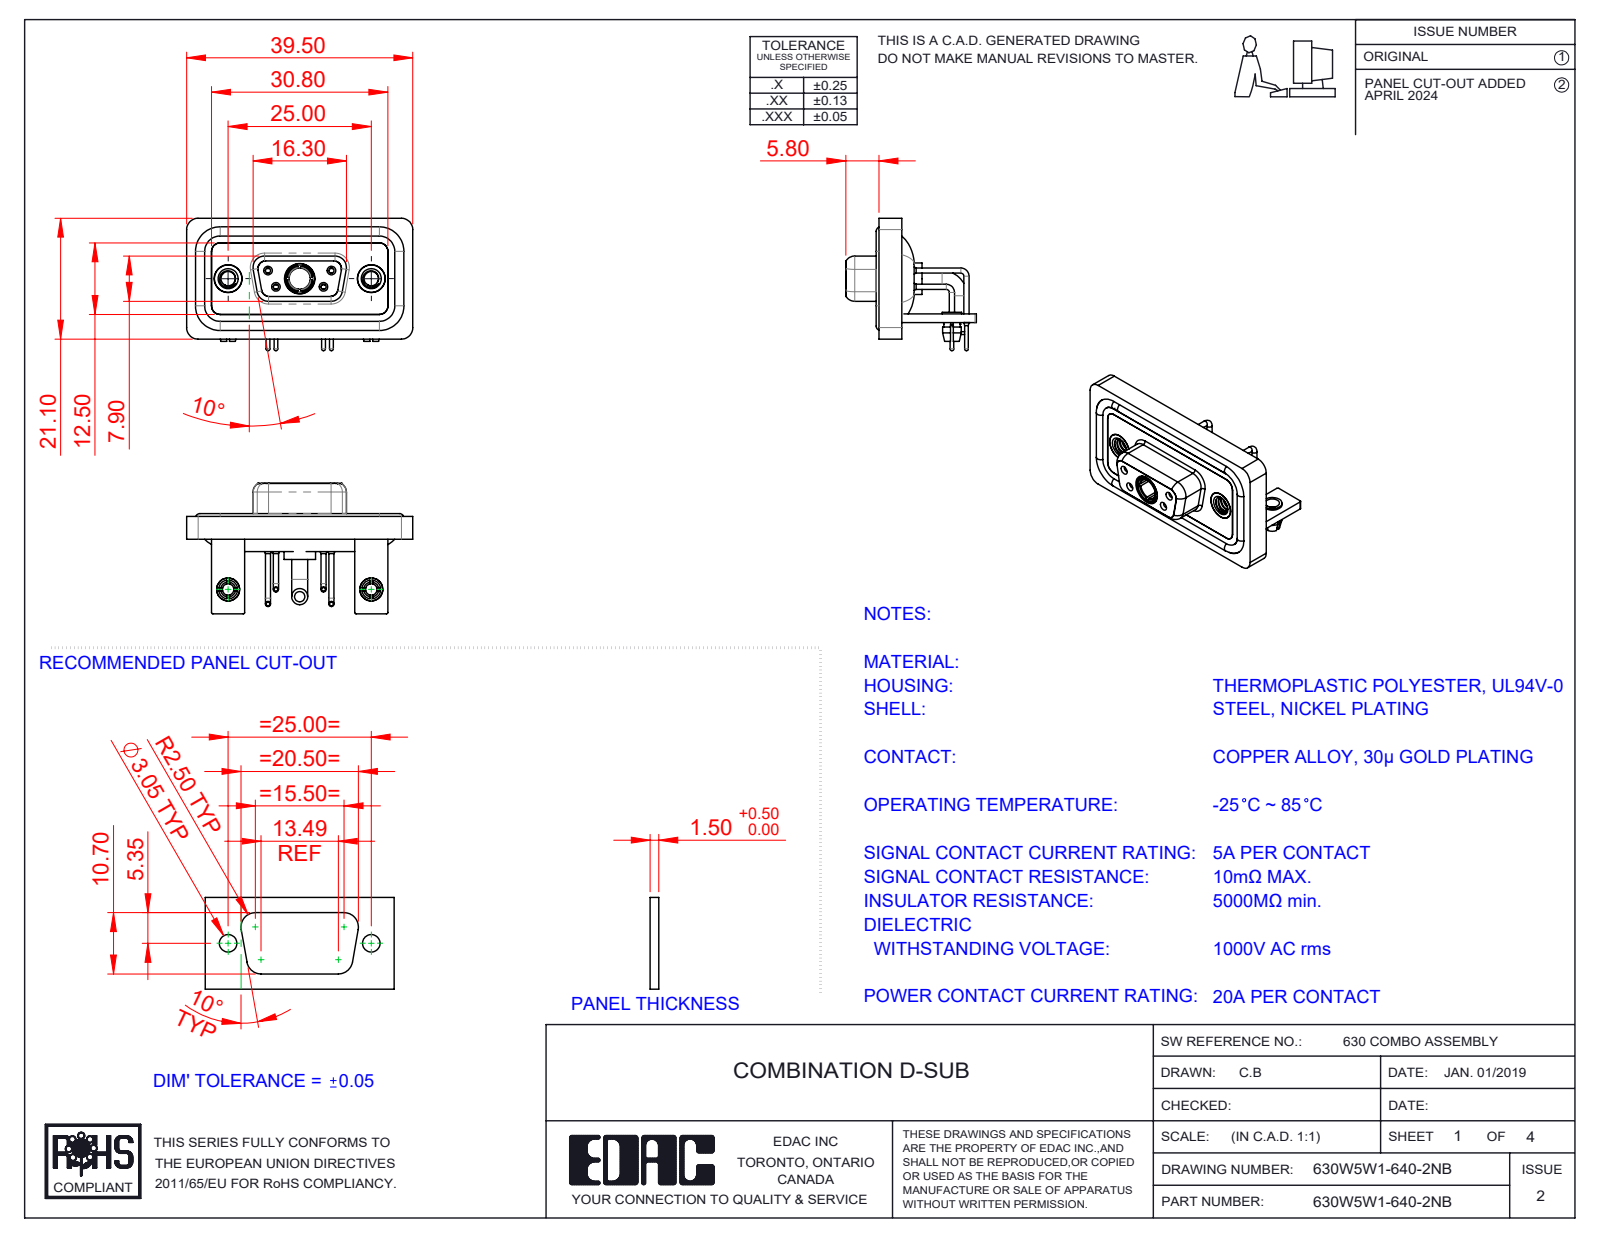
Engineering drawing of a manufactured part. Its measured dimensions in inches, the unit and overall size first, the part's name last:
Units: inches
Overall size (bounding box): 1.555 × 0.91 × 0.898
Round holes (diameter × count): ⌀0.079 ×6, ⌀0.035 ×4, ⌀0.043 ×4, ⌀0.059 ×4, ⌀0.098 ×4, ⌀0.191 ×3, ⌀0.063 ×2, ⌀0.067 ×2, ⌀0.126 ×2, ⌀0.157 ×2, ⌀0.159 ×2, ⌀0.197 ×2
Round bosses / shafts (diameter × count): ⌀0.063 ×6, ⌀0.035 ×4, ⌀0.026 ×4, ⌀0.195 ×2, ⌀0.189 ×2, ⌀0.157 ×2, ⌀0.134 ×2, ⌀0.13 ×2
Partial cylindrical surfaces — rounded edges, fillets, slot ends (radius × count): R0.079 ×19, R0.059 ×18, R0.01 ×16, R0.053 ×8, R0.063 ×8, R0.02 ×5, R0.024 ×4, R0.026 ×4
Main face-to-face distances: 0.016, 0.114, 0.059, 0.071, 0.043, 0.146, 0.063, 0.031, 0.098, 0.122
Hole centre spacings: 0.124, 0.225, 0.28, 0.492, 0.713, 0.984, 0.173, 0.173
Volume: 0.319 in³ · Surface area: 13.63 in²
Bodies: 17 solids, 810 faces (262 planar, 359 cylindrical, 189 other)
Part name (STEP PRODUCT): 630Combo Contact Row 1_50 Contacts; 630Combo Housing_5W1; 630Combo Board Lock_50 Contacts; 630Combo Contact Row 2_50 Contacts (+7 more)
STEP written by: SolidWorks 2023 (CONFIG_CONTROL_DESIGN)
